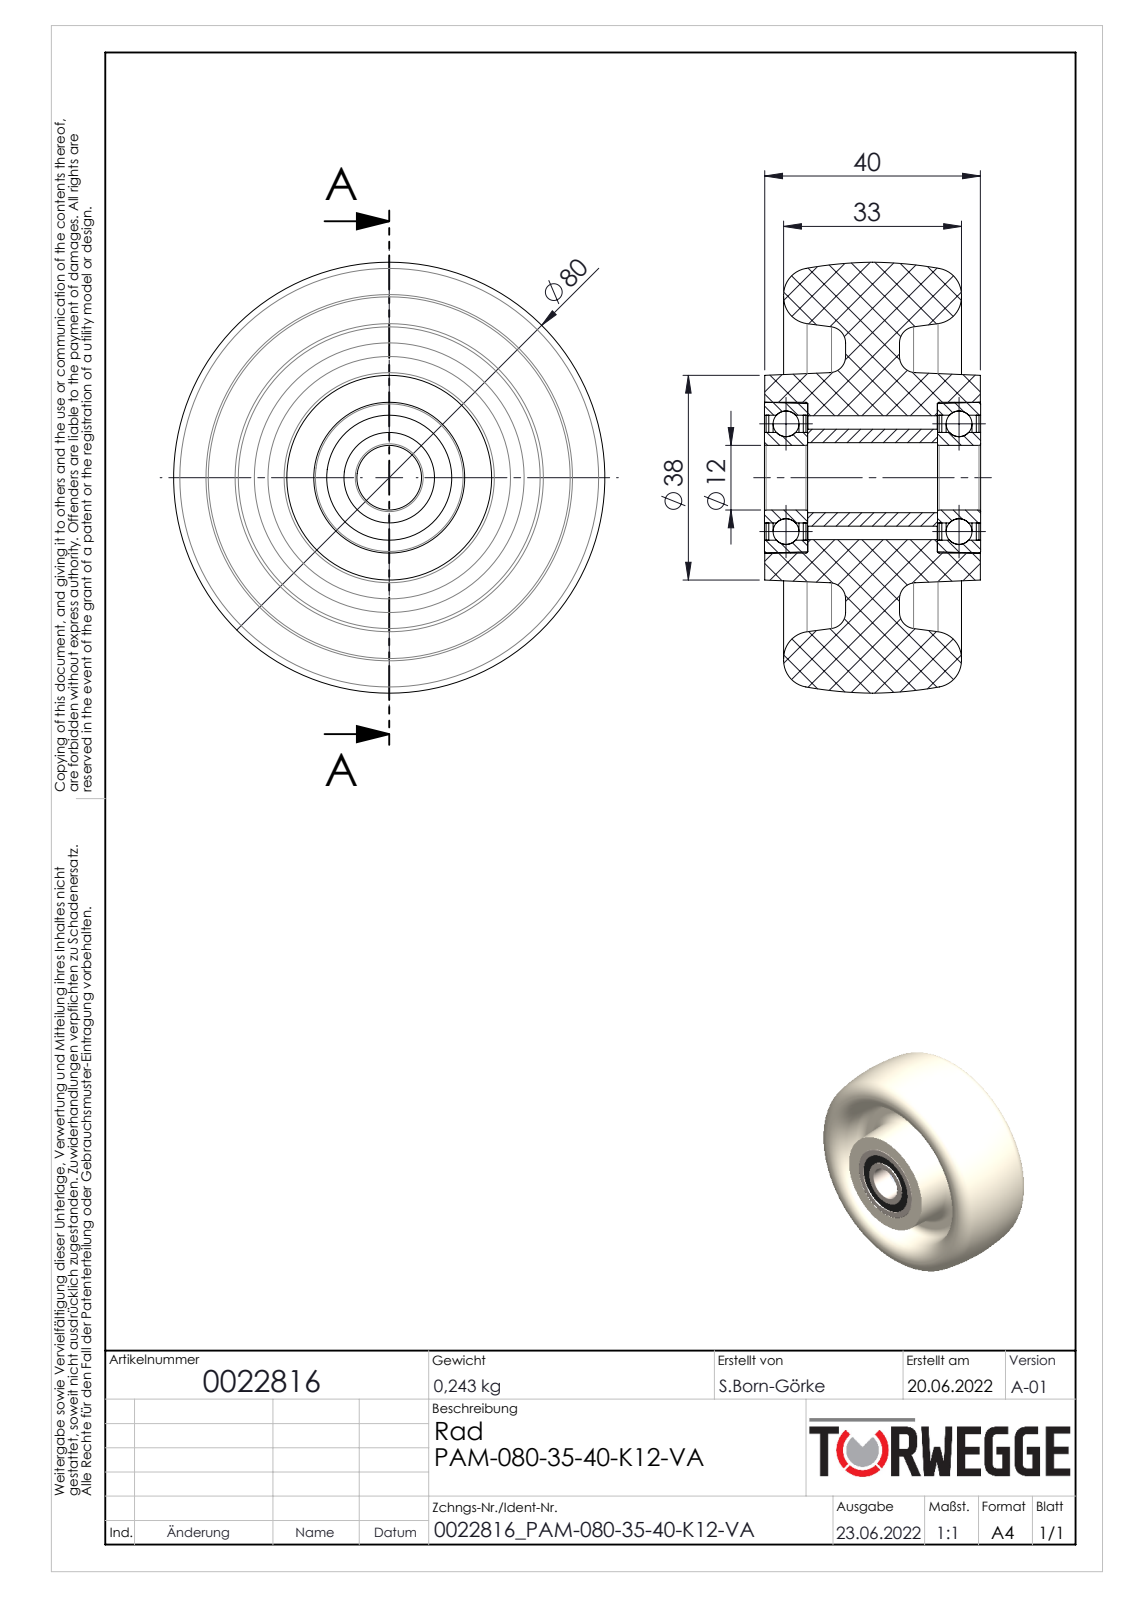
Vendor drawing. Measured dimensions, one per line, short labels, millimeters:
name: 0022816
written by: SolidWorks 2020 (AUTOMOTIVE_DESIGN)
unit: mm
bodies: 12 solids, 142 faces (24 planar, 46 cylindrical, 72 other)
size: 80 × 80 × 40.1
volume: 125 189 mm³; area: 36 449 mm²
holes: 1× ⌀12, 1× ⌀13, 1× ⌀16.8, 1× ⌀23, 1× ⌀23.2
bosses: 1× ⌀28, 1× ⌀18
face distances: 32.1, 32.05, 8, 0.8, 7.2, 7.7, 0.5, 6.9, 7.95, 15
